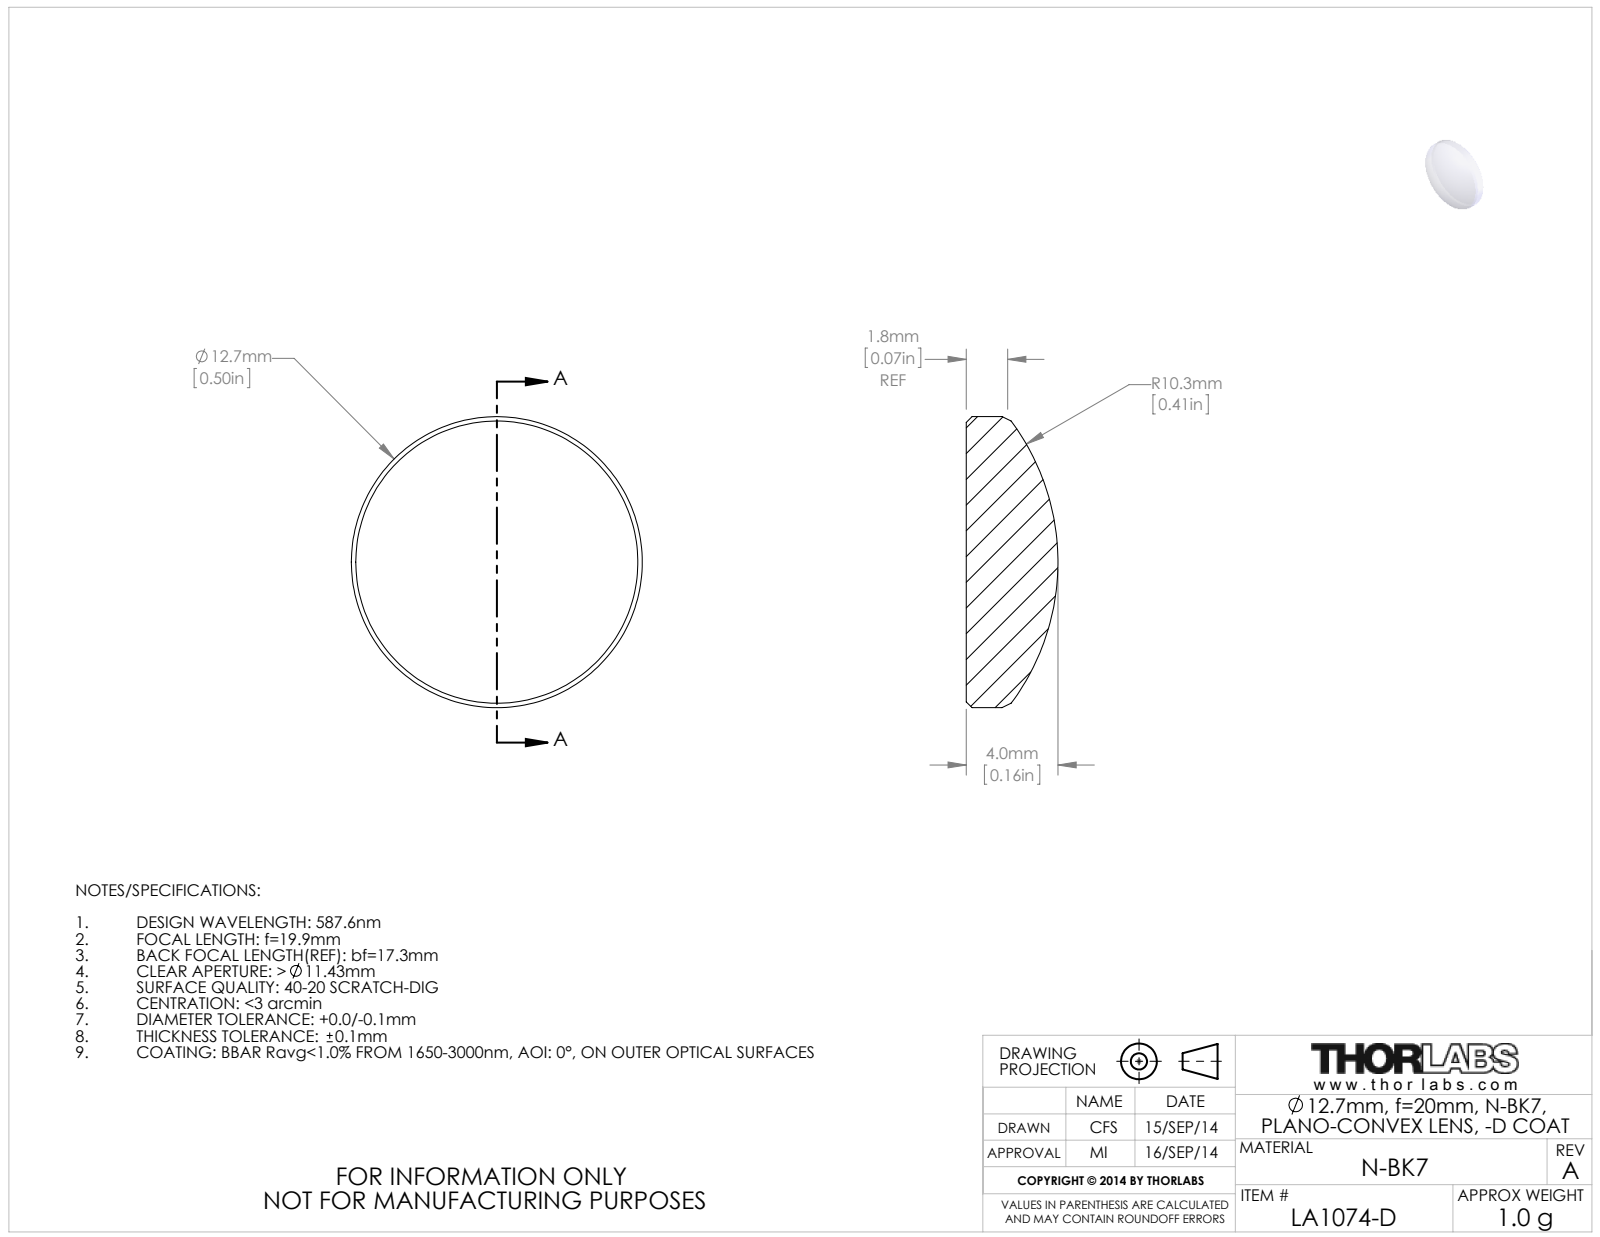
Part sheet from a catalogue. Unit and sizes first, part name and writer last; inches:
Units: inches
Overall size (bounding box): 0.5 × 0.5 × 0.157
Round bosses / shafts (diameter × count): ⌀0.5 ×1
Volume: 0.023 in³ · Surface area: 0.515 in²
Bodies: 1 solid, 9 faces (1 planar, 2 cylindrical, 6 other)
Part name (STEP PRODUCT): TTN031779-E0W
STEP written by: SolidWorks 2014 (CONFIG_CONTROL_DESIGN)
